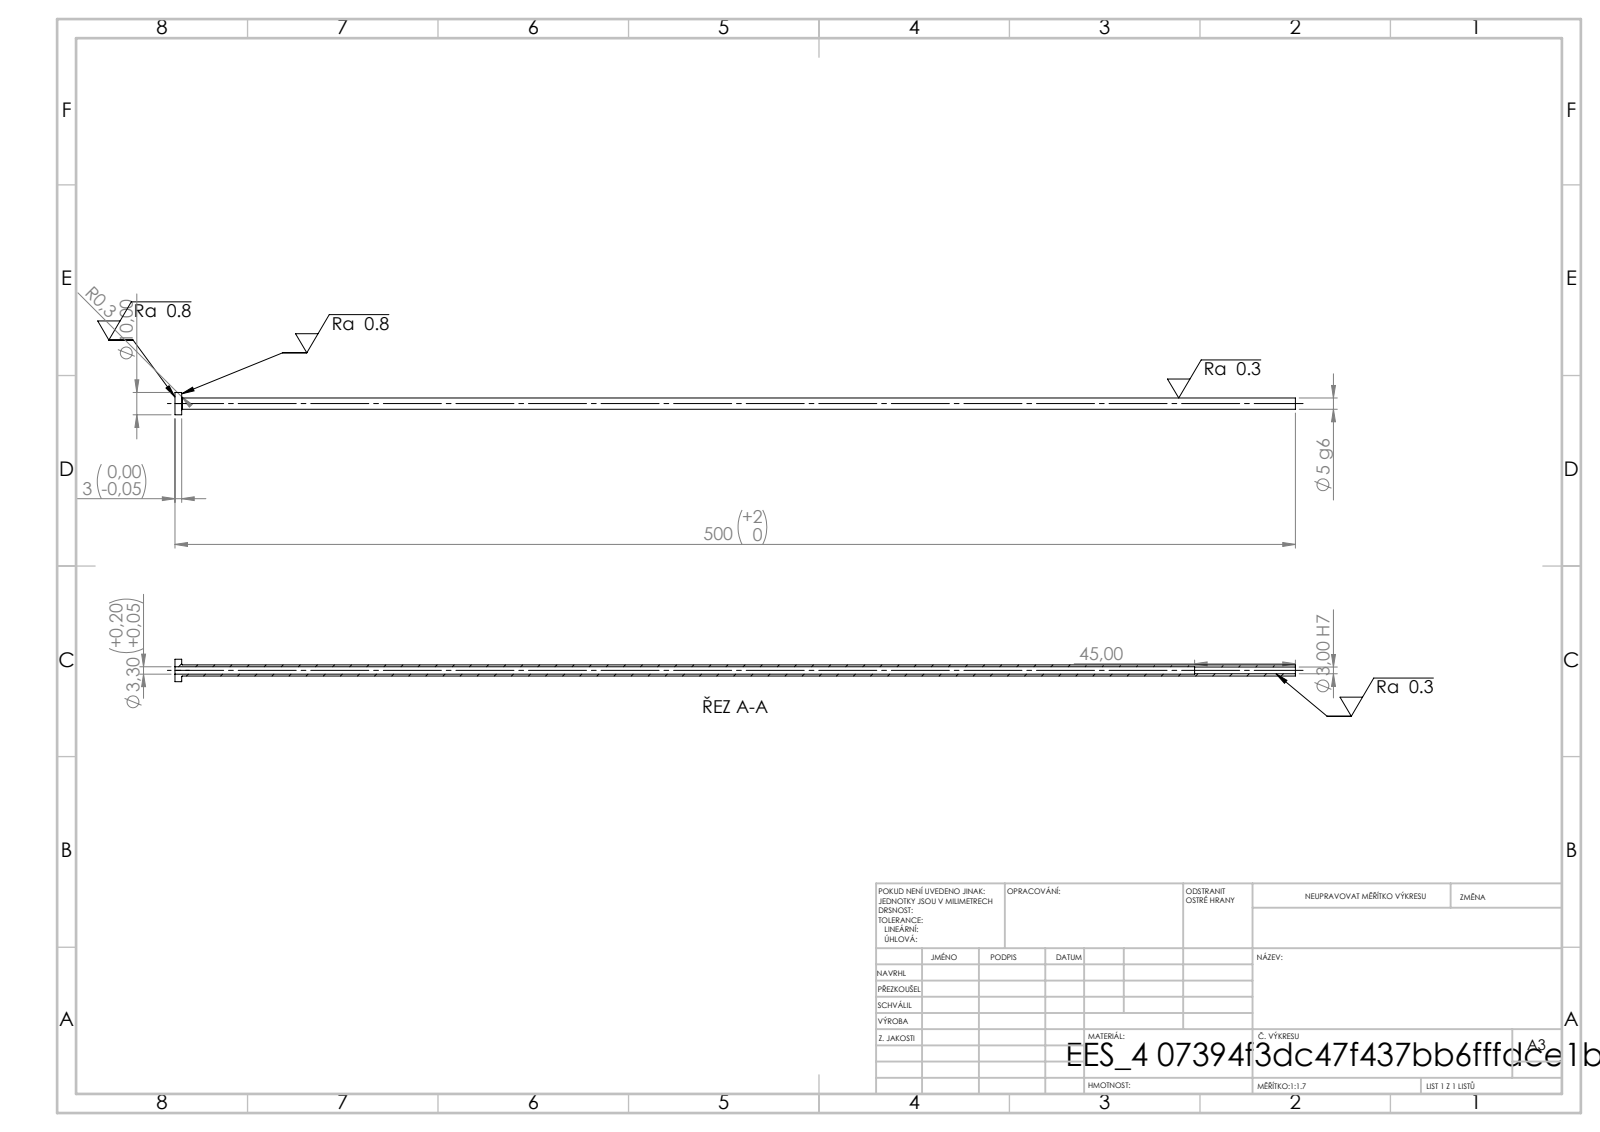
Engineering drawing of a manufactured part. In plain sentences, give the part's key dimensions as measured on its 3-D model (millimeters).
Its 3-D file was written by "SolidWorks 2019 (CONFIG_CONTROL_DESIGN)". It is 1 solid with 14 faces: 4 planar, 8 cylindrical and 2 other. Overall it measures 500 by 10 by 10 millimeters. Its volume is 5 785 cubic millimeters and its surface area 13 183 square millimeters. Round holes: 1 of diameter 3, 1 of diameter 3.3. Round bosses or shafts: 1 of diameter 10, 1 of diameter 5. The main face-to-face distances are 3, 500, 497, 455, 452, 45.
